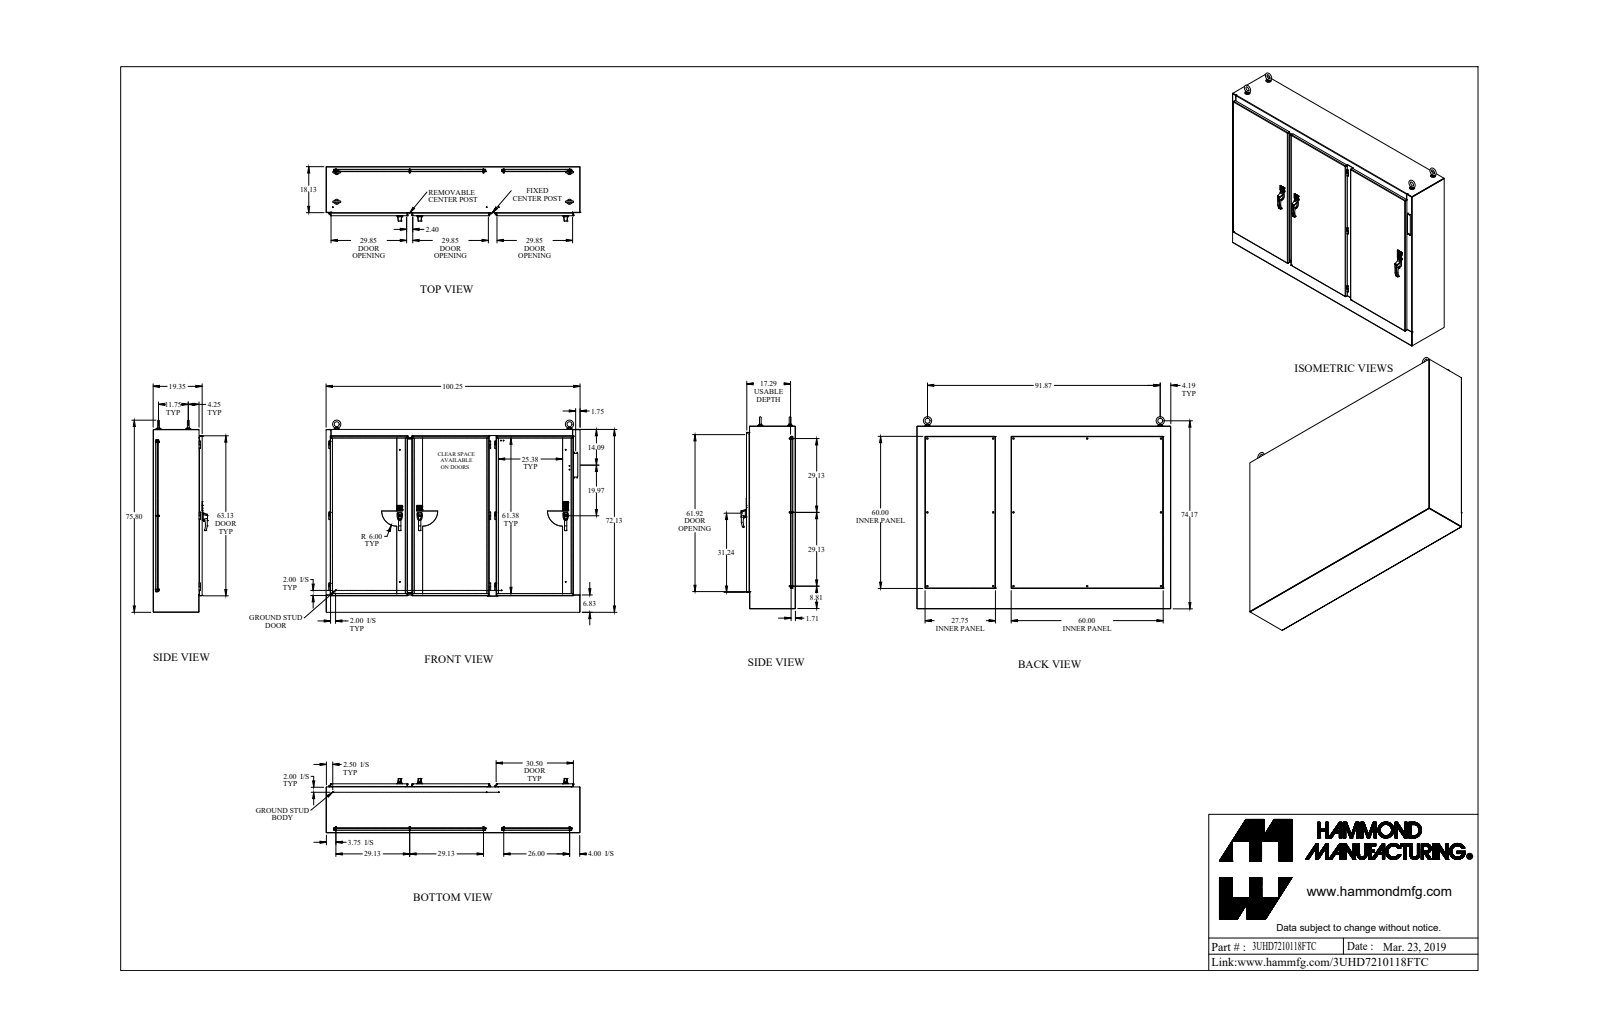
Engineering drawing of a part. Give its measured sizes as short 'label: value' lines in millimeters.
name: 3UHD7210118FTC
written by: SolidWorks 2018 (AUTOMOTIVE_DESIGN)
unit: mm
bodies: 306 solids, 4260 faces (2594 planar, 1193 cylindrical, 473 other)
size: 2546.4 × 1925.3 × 545.2
volume: 55 990 000 mm³; area: 41 930 000 mm²
holes: 22× ⌀6.4, 19× ⌀5, 17× ⌀7.8, 12× ⌀7.1, 9× ⌀8, 9× ⌀8.9, 9× ⌀11.3, 8× ⌀22.2, 6× ⌀6.5, 6× ⌀6.8, 6× ⌀7.1, 6× ⌀9.9
bosses: 22× ⌀25.4, 18× ⌀6.4, 15× ⌀9.5, 14× ⌀16.5, 14× ⌀8.4, 12× ⌀7.1, 10× ⌀6.2, 9× ⌀15.9
rounds: 71× R1.5, 60× R3.2, 50× R4.7, 48× R0.4, 41× R12.7, 18× R0.8, 18× R2.3, 16× R3.3
face distances: 3.2, 1.8, 442.7, 492, 488.8, 490.1, 487, 49.2, 46, 440.9
hole spacings: 739.8, 1479.6, 54, 199.9, 298.5, 739.8, 1463.8, 1654.2
